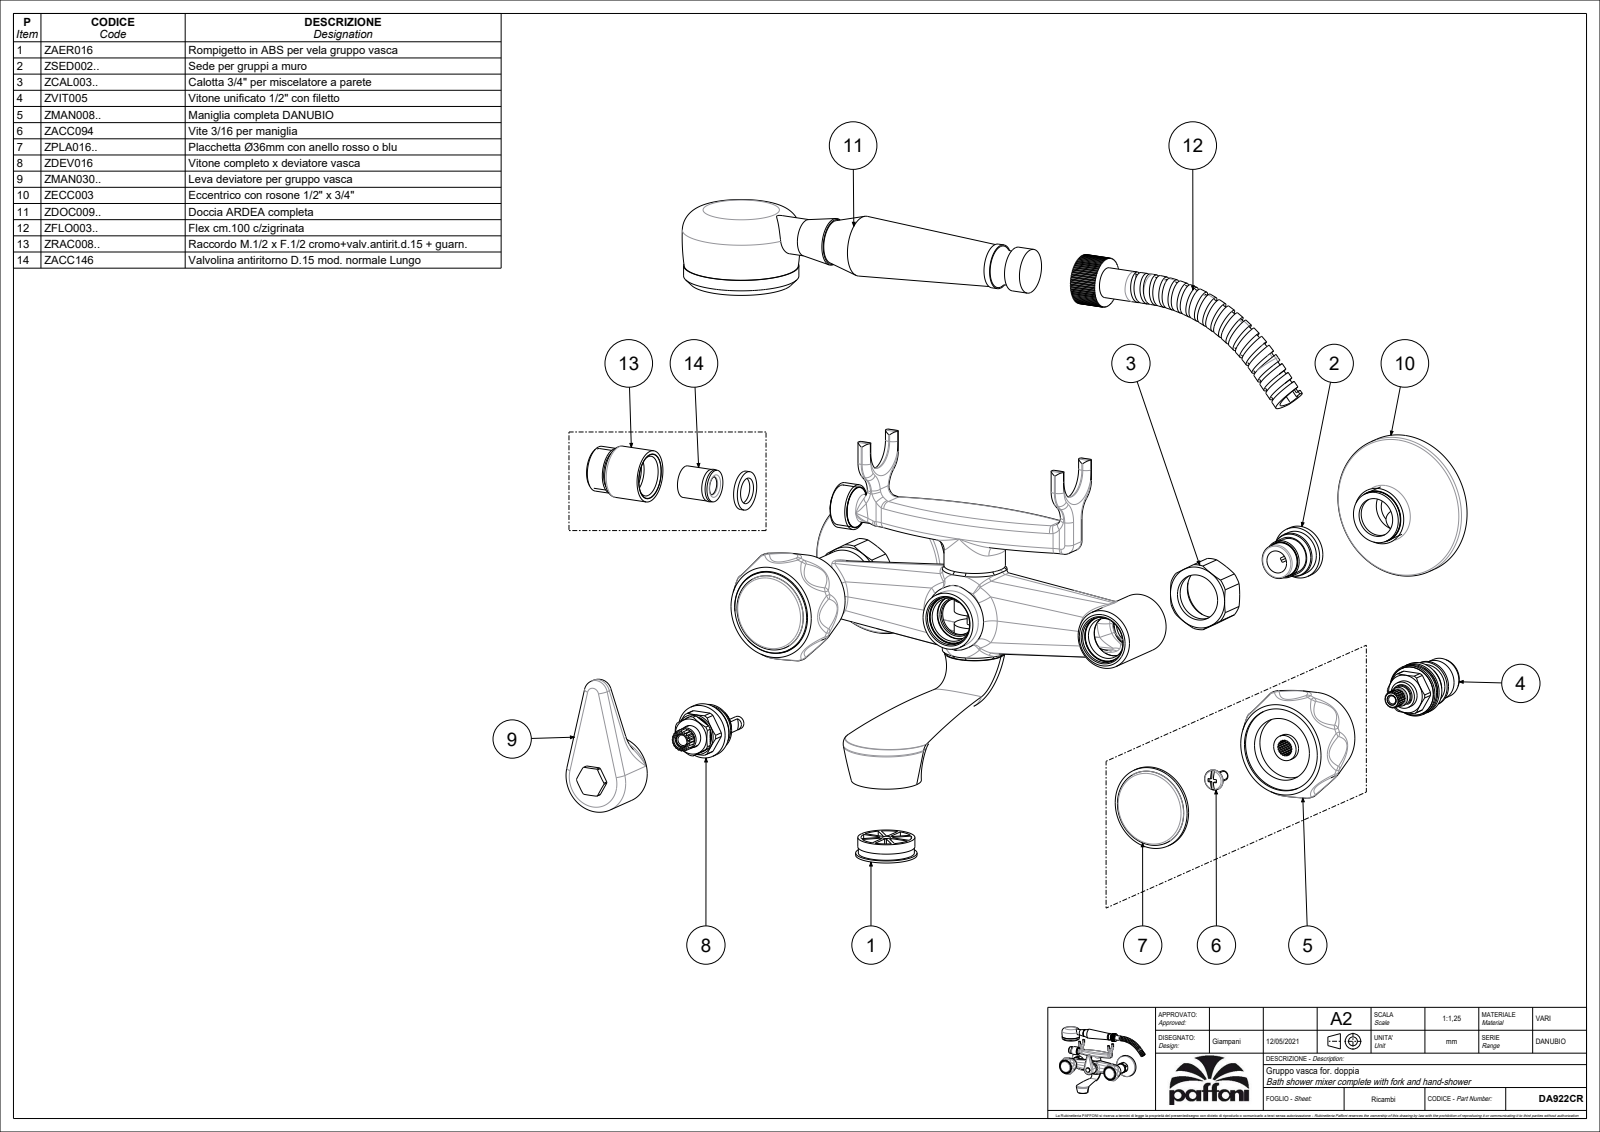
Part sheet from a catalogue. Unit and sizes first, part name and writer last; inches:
Units: inches
Overall size (bounding box): 11.654 × 6.767 × 6.102
Round holes (diameter × count): ⌀0.413 ×3, ⌀0.984 ×3, ⌀0.709 ×2, ⌀0.846 ×2, ⌀0.949 ×2, ⌀1.051 ×2, ⌀1.409 ×2, ⌀1.535 ×2, ⌀2.575 ×2, ⌀0.157 ×1, ⌀0.276 ×1, ⌀0.335 ×1
Round bosses / shafts (diameter × count): ⌀0.807 ×3, ⌀2.598 ×2, ⌀1.516 ×2, ⌀1.201 ×2, ⌀1.083 ×2, ⌀1.008 ×2, ⌀0.945 ×2, ⌀0.886 ×2
Partial cylindrical surfaces — rounded edges, fillets, slot ends (radius × count): R0.039 ×28, R0.839 ×16, R0.118 ×5, R0.138 ×4, R0.236 ×3, R0.61 ×3, R0.02 ×2, R0.197 ×2
Main face-to-face distances: 1.142, 0.236, 0.264, 1.969, 0.827, 0.374, 0.26, 3.11, 0.02, 0.059
Hole centre spacings: 3.11, 3.228, 6.22
Volume: 20.84 in³ · Surface area: 264.6 in²
Bodies: 3 solids, 1700 faces (564 planar, 394 cylindrical, 742 other)
Part name (STEP PRODUCT): DA024CR
STEP written by: CREO PARAMETRIC BY PTC INC, 2020044 (CONFIG_CONTROL_DESIGN)
